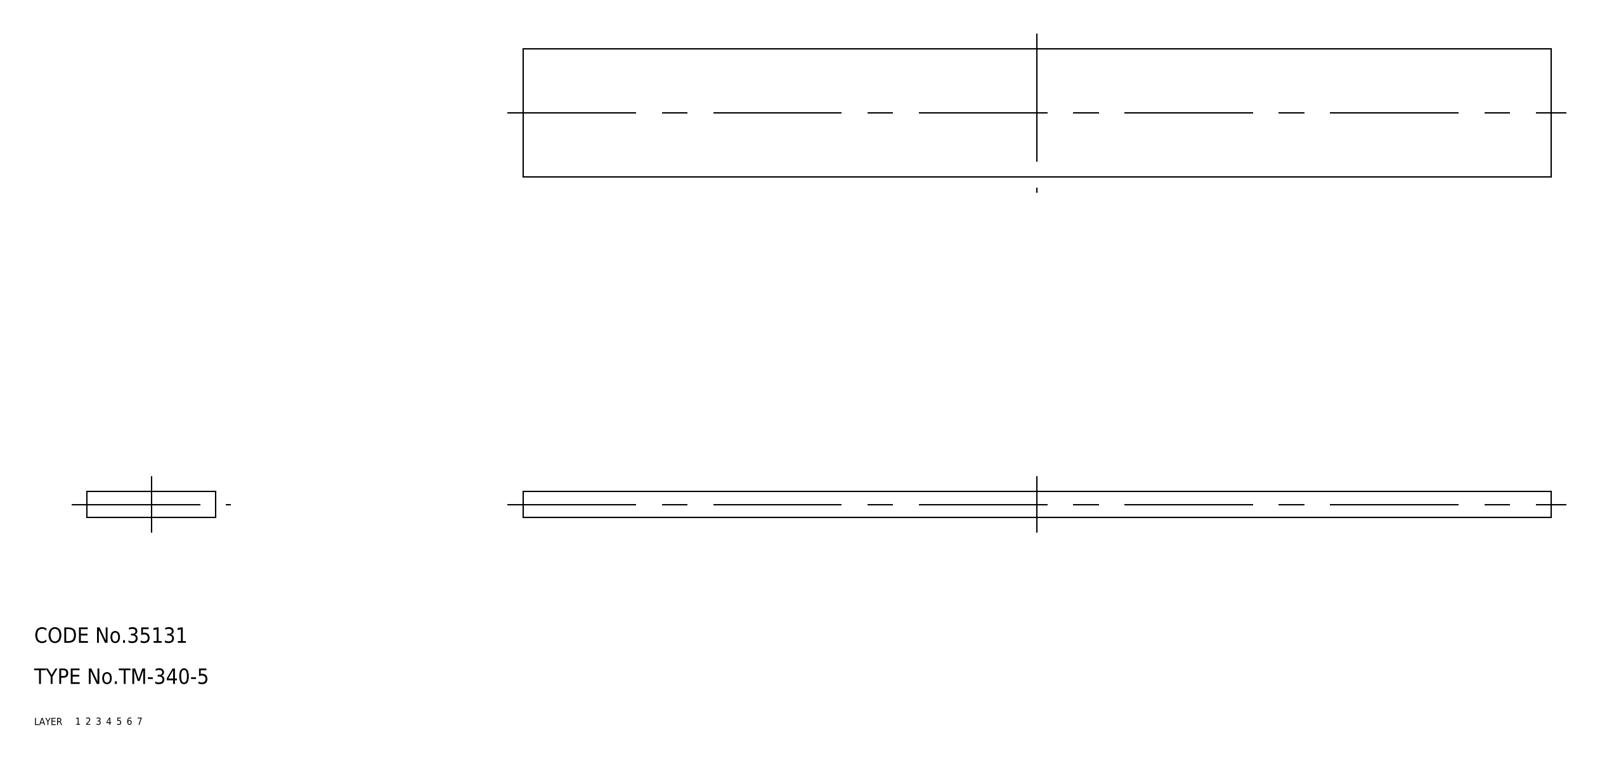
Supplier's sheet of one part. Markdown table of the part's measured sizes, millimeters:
| quantity | value |
| --- | --- |
| part name | rubber foam; TM_340_5 |
| STEP written by | SolidWorks 2015 (AUTOMOTIVE_DESIGN) |
| units | millimeters |
| bodies | 1 solid, 6 faces (6 planar, 0 cylindrical, 0 other) |
| overall size | 200 × 25 × 5 |
| volume | 25 000 mm³ |
| surface area | 12 250 mm² |
| main face-to-face distances | 5, 25, 200 |
